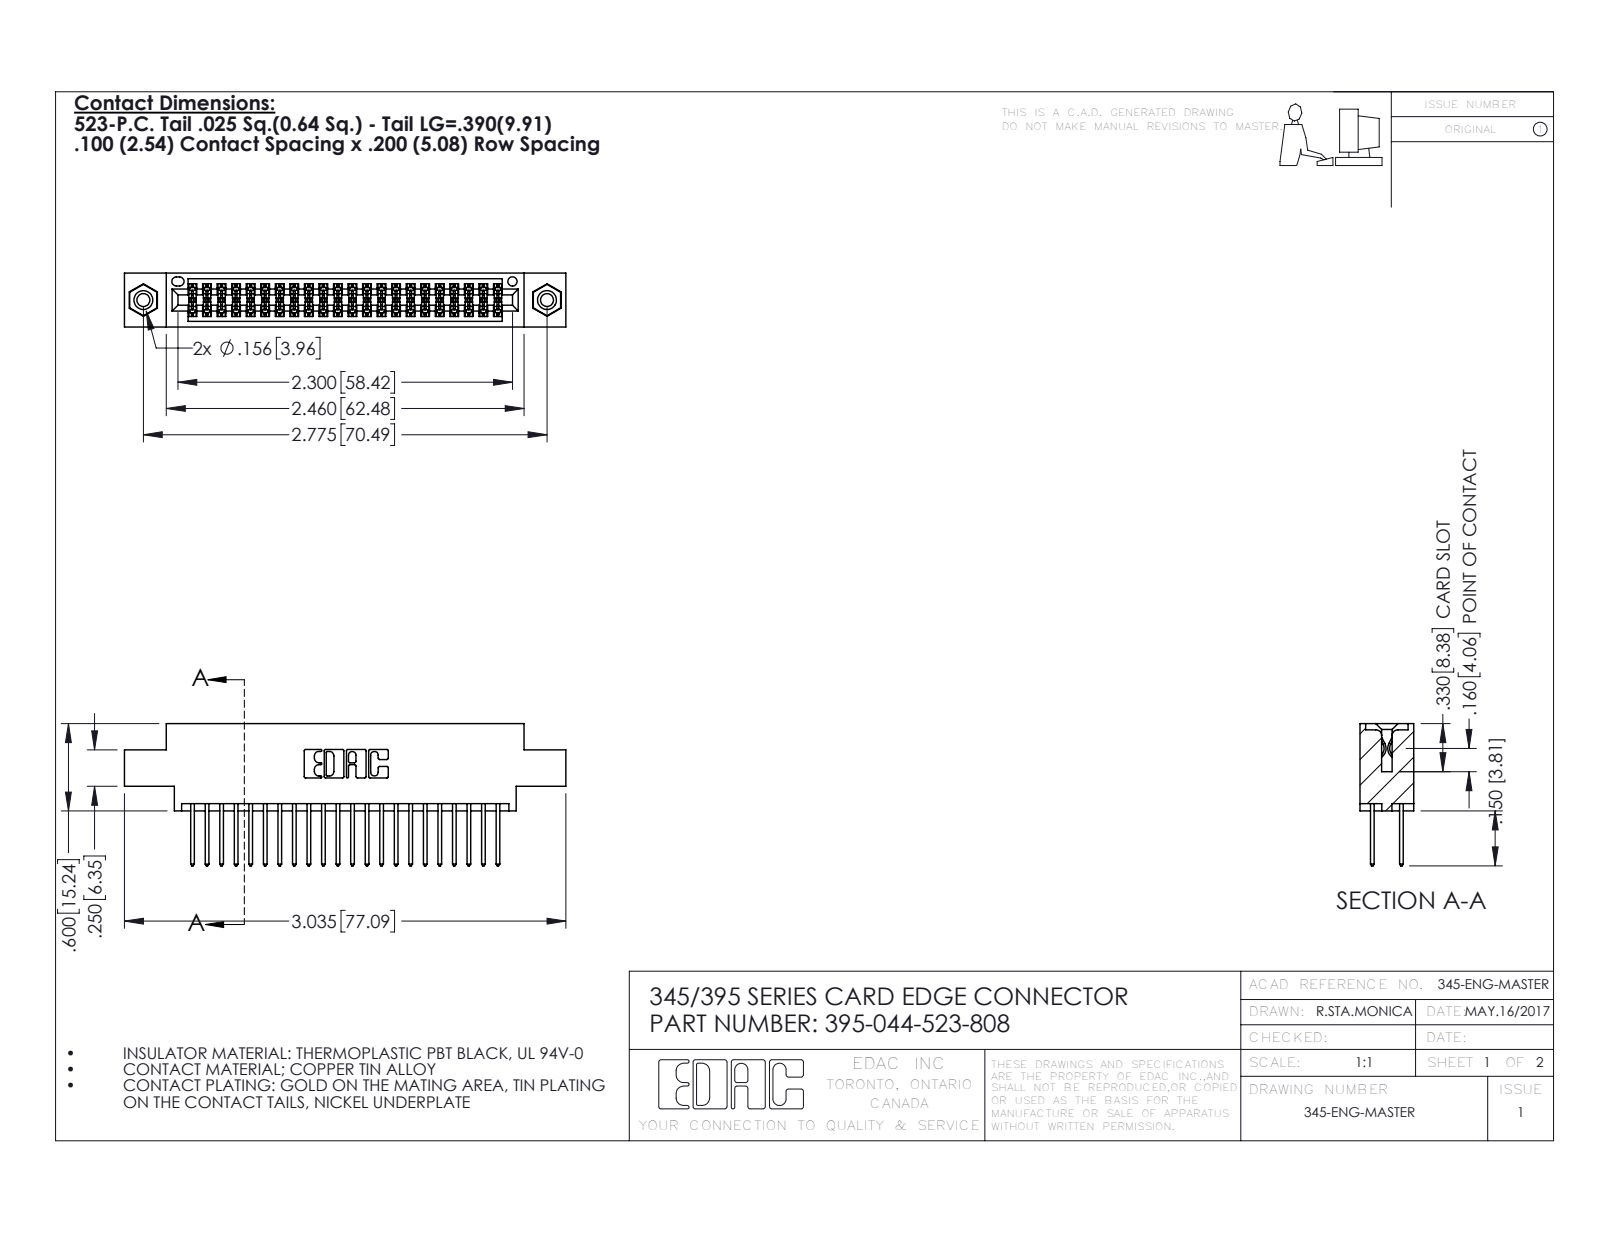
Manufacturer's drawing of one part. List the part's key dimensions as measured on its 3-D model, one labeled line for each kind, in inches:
Part name (STEP PRODUCT): 345 Part_0.170 Offset - 0.156 Dia-TI; 345-250-001_345-250-003-102; 395-044-523-808; 345-292-001_345-293-123
STEP written by: SolidWorks 2016 (CONFIG_CONTROL_DESIGN)
Units: inches
Bodies: 47 solids, 2390 faces (1568 planar, 806 cylindrical, 16 other)
Overall size (bounding box): 3.035 × 0.977 × 0.37
Volume: 0.444 in³ · Surface area: 16.93 in²
Round holes (diameter × count): ⌀0.089 ×2, ⌀0.125 ×2, ⌀0.156 ×2, ⌀0.064 ×1
Round bosses / shafts (diameter × count): ⌀0.155 ×2
Partial cylindrical surfaces — rounded edges, fillets, slot ends (radius × count): R0.006 ×66, R0.01 ×44, R0.01 ×22, R0.007 ×6, R0.031 ×6, R0.026 ×3, R0.014 ×2, R0.019 ×2
Main face-to-face distances: 0.072, 0.298, 0.2, 0.37, 0.098, 0.272, 0.025, 0.225, 0.175, 0.149
Hole centre spacings: 0.27, 2.541, 2.775
